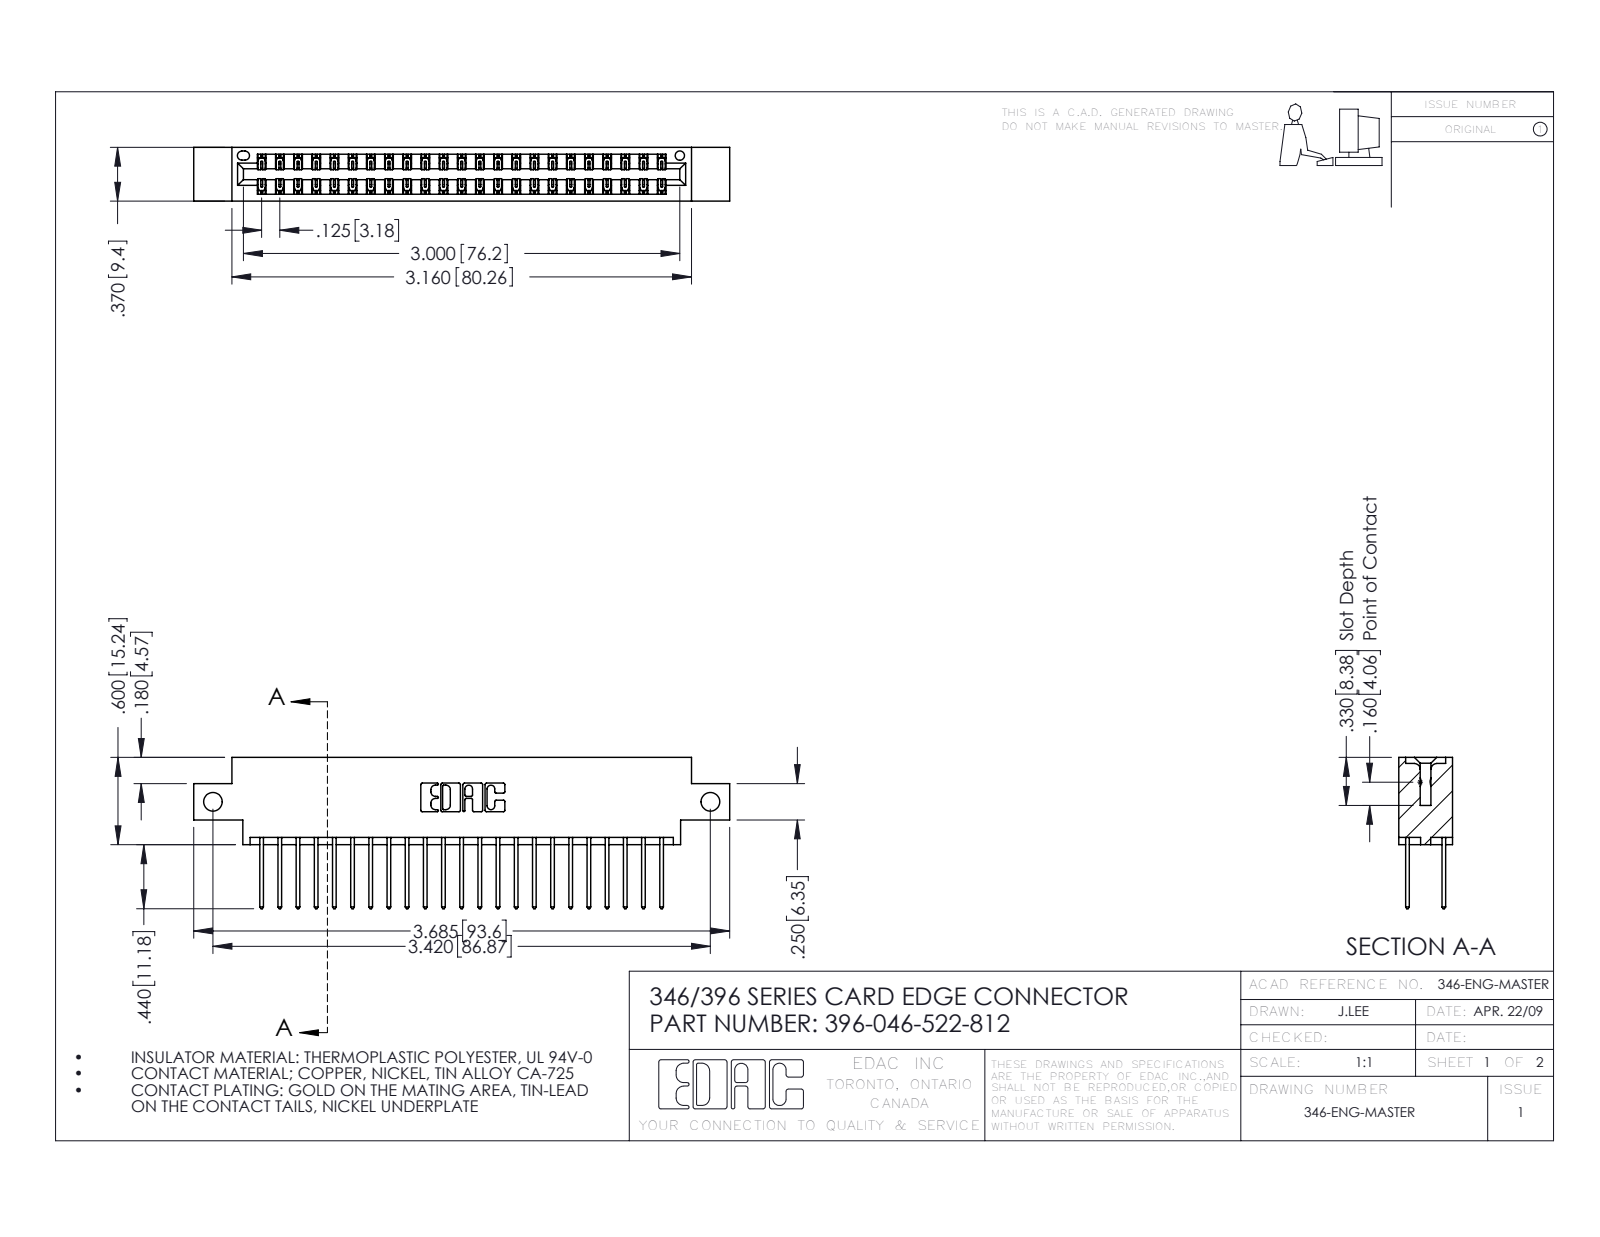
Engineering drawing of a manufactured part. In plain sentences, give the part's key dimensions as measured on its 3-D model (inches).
The part is named "396-046-522-812; 346 Part_0.170 Offset - Side Mount; 345-292-001_345-293-122". Its 3-D file was written by "SolidWorks 2016 (CONFIG_CONTROL_DESIGN)". It is 47 solids with 2518 faces: 1690 planar, 828 cylindrical and 0 other. Overall it measures 3.685 by 1.04 by 0.37 inches. Its volume is 0.54 cubic inches and its surface area 19.32 square inches. Round holes: 2 of diameter 0.128, 1 of diameter 0.064. Partial cylindrical surfaces (rounded edges, fillets, slot ends): 69 of radius 0.006, 46 of radius 0.01, 22 of radius 0.01, 6 of radius 0.007, 6 of radius 0.031, 3 of radius 0.026, 2 of radius 0.014, 2 of radius 0.022. The main face-to-face distances are 0.048, 0.322, 0.25, 0.37, 0.072, 0.298, 0.025, 0.275, 0.148, 0.222. The hole center spacings are 3.42.
